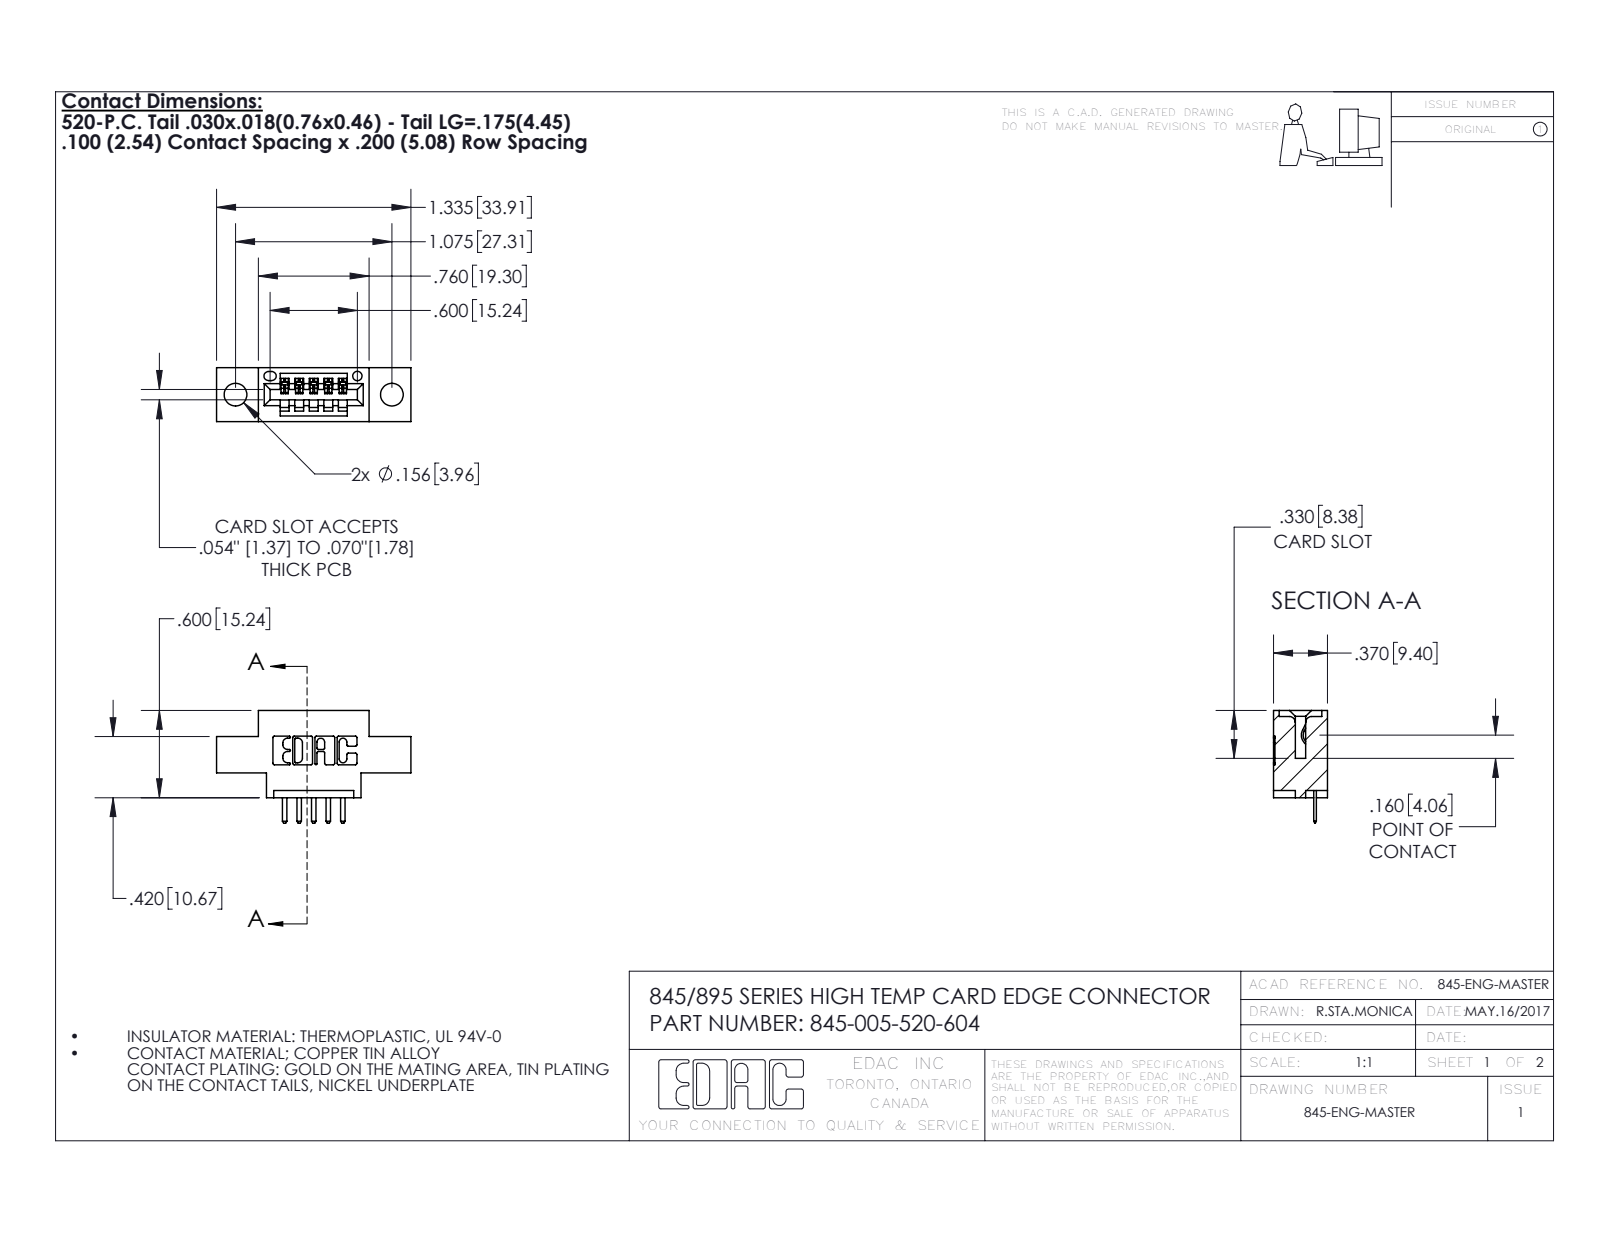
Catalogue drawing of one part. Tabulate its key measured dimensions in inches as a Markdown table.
| quantity | value |
| --- | --- |
| part name | 345 Part_0.170 Offset - 0.156 Dia-TH; 345-005-520-604; 345-292-001_345-293-120 |
| STEP written by | SolidWorks 2016 (CONFIG_CONTROL_DESIGN) |
| units | inches |
| bodies | 6 solids, 440 faces (294 planar, 146 cylindrical, 0 other) |
| overall size | 1.335 × 0.775 × 0.37 |
| volume | 0.165 in³ |
| surface area | 4.613 in² |
| round holes (diameter × count) | 0.156 × 2, 0.064 × 1 |
| partial cylindrical surfaces (radius × count) | 0.01 × 22, 0.01 × 12, 0.006 × 10, 0.007 × 6, 0.031 × 6, 0.026 × 3, 0.031 × 2, 0.04 × 2 |
| main face-to-face distances | 0.37, 0.2, 0.1, 0.298, 0.072, 0.25, 0.025, 0.06, 0.55, 0.15 |
| hole center spacings | 0.27, 0.847, 1.075 |
